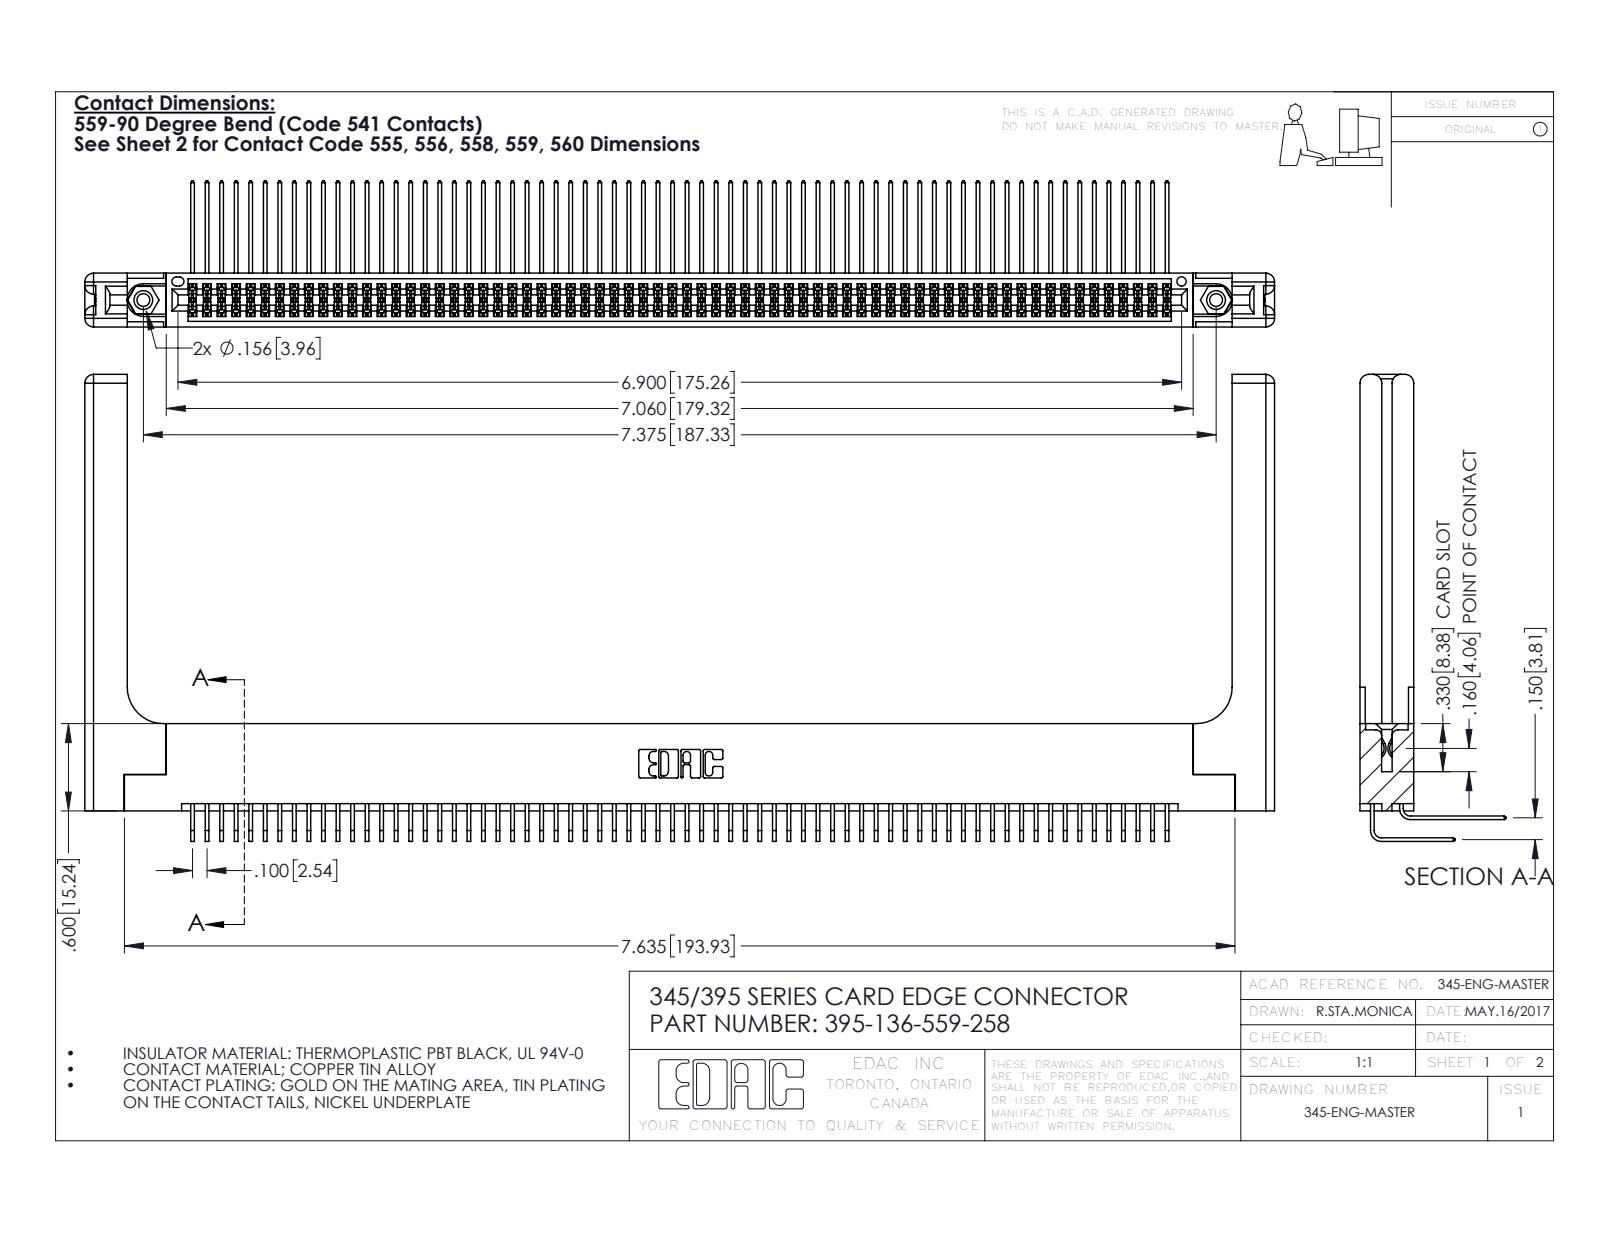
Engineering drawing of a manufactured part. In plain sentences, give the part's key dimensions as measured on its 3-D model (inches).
The part is named "345-220-058_345-220-058; 395-136-559-258; 345-292-001_559 Tail - 2; 345 Part_Flush Mounting Lugs - 0.156 Dia-TH (+2 more)". Its 3-D file was written by "SolidWorks 2016 (CONFIG_CONTROL_DESIGN)". It is 141 solids with 7454 faces: 4988 planar, 2406 cylindrical and 60 other. Overall it measures 8.179 by 3.209 by 1.005 inches. Its volume is 1.811 cubic inches and its surface area 62.93 square inches. Round holes: 2 of diameter 0.089, 2 of diameter 0.125, 2 of diameter 0.156, 1 of diameter 0.064. Round bosses or shafts: 2 of diameter 0.155. Partial cylindrical surfaces (rounded edges, fillets, slot ends): 271 of radius 0.006, 22 of radius 0.01, 16 of radius 0.06, 6 of radius 0.007, 6 of radius 0.031, 3 of radius 0.026, 2 of radius 0.014, 2 of radius 0.019. The main face-to-face distances are 0.072, 0.298, 0.37, 0.2, 0.098, 0.272, 0.025, 0.225, 0.175, 0.15. The hole center spacings are 0.27, 7.139, 7.375.
